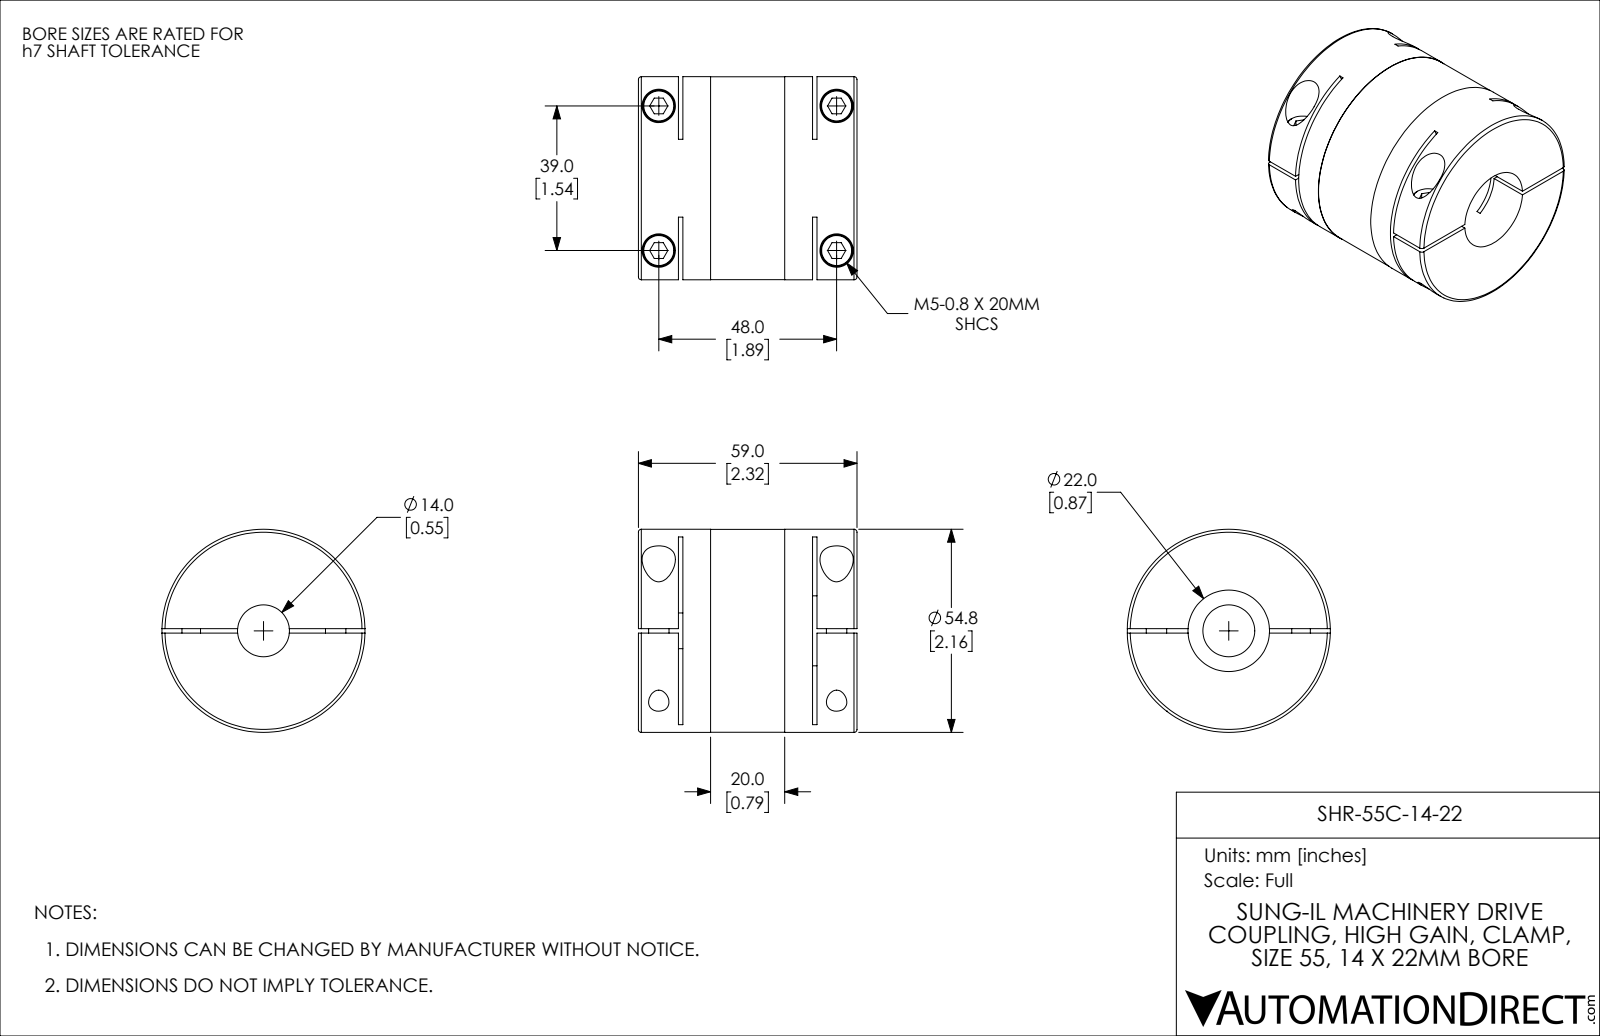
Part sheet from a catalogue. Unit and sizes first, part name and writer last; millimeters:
Units: millimetres
Overall size (bounding box): 59 × 54.8 × 54.8
Round holes (diameter × count): ⌀5.5 ×4, ⌀9 ×4, ⌀14 ×1, ⌀22 ×1, ⌀24 ×1
Round bosses / shafts (diameter × count): ⌀8.5 ×4, ⌀5 ×2, ⌀54.8 ×1, ⌀54.7 ×1
Partial cylindrical surfaces — rounded edges, fillets, slot ends (radius × count): R60 ×2
Main face-to-face distances: 1.2, 12, 47, 10.8, 48.2, 36.2, 59, 35, 37.4, 19.5
Hole centre spacings: 39, 48, 61.85
Volume: 112 159 mm³ · Surface area: 28 890 mm²
Bodies: 1 solid, 144 faces (70 planar, 58 cylindrical, 16 other)
Part name (STEP PRODUCT): SHR-55C-14-22
STEP written by: SolidWorks 2021 (CONFIG_CONTROL_DESIGN)
